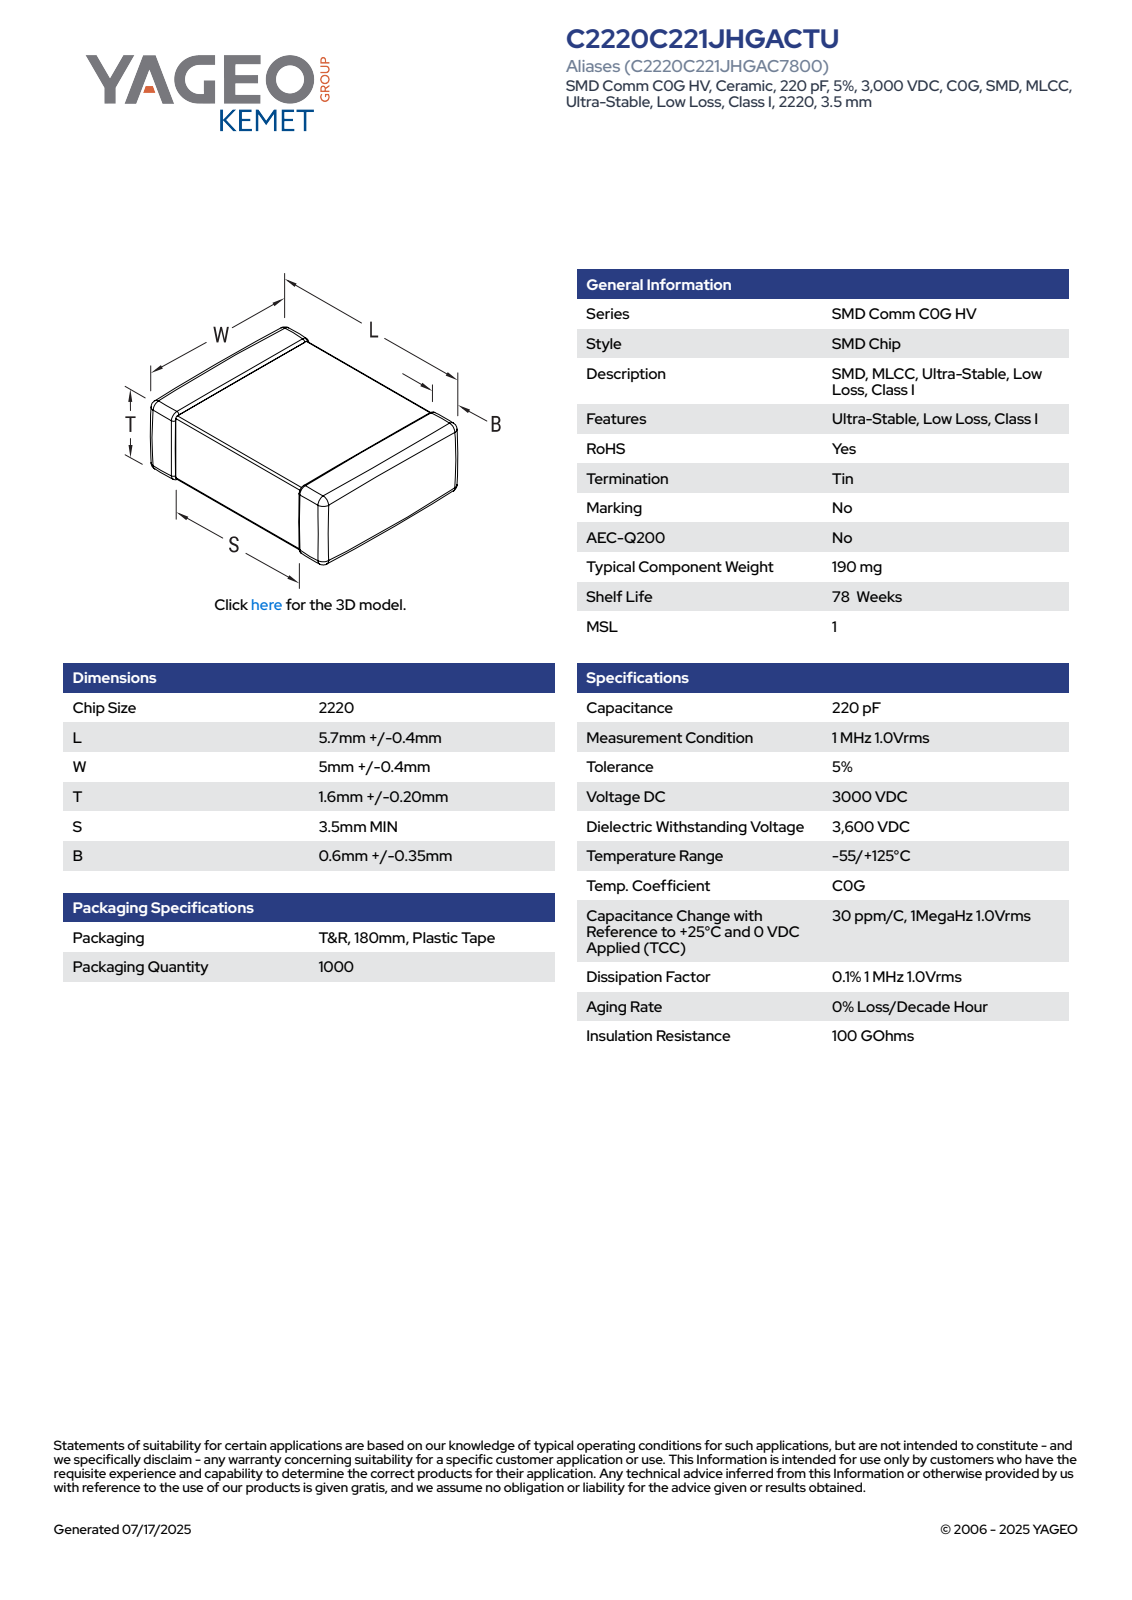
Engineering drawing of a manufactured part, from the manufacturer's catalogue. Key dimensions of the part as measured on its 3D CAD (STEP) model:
Part name (STEP PRODUCT): CCS_CCSTDNOS_2220_L6.1W5.4T1.8B0.95
STEP written by: SolidWorks 2014 (AUTOMOTIVE_DESIGN)
Units: millimetres
Bodies: 4 solids, 125 faces (71 planar, 38 cylindrical, 16 other)
Overall size (bounding box): 6.1 × 5.4 × 1.8
Volume: 52 mm³ · Surface area: 104 mm²
Partial cylindrical surfaces — rounded edges, fillets, slot ends (radius × count): R0.11 ×24
Main face-to-face distances: 1.58, 1.69, 6.1, 1.8, 5.18, 5.29, 5.4, 2.66, 2.74, 2.55
